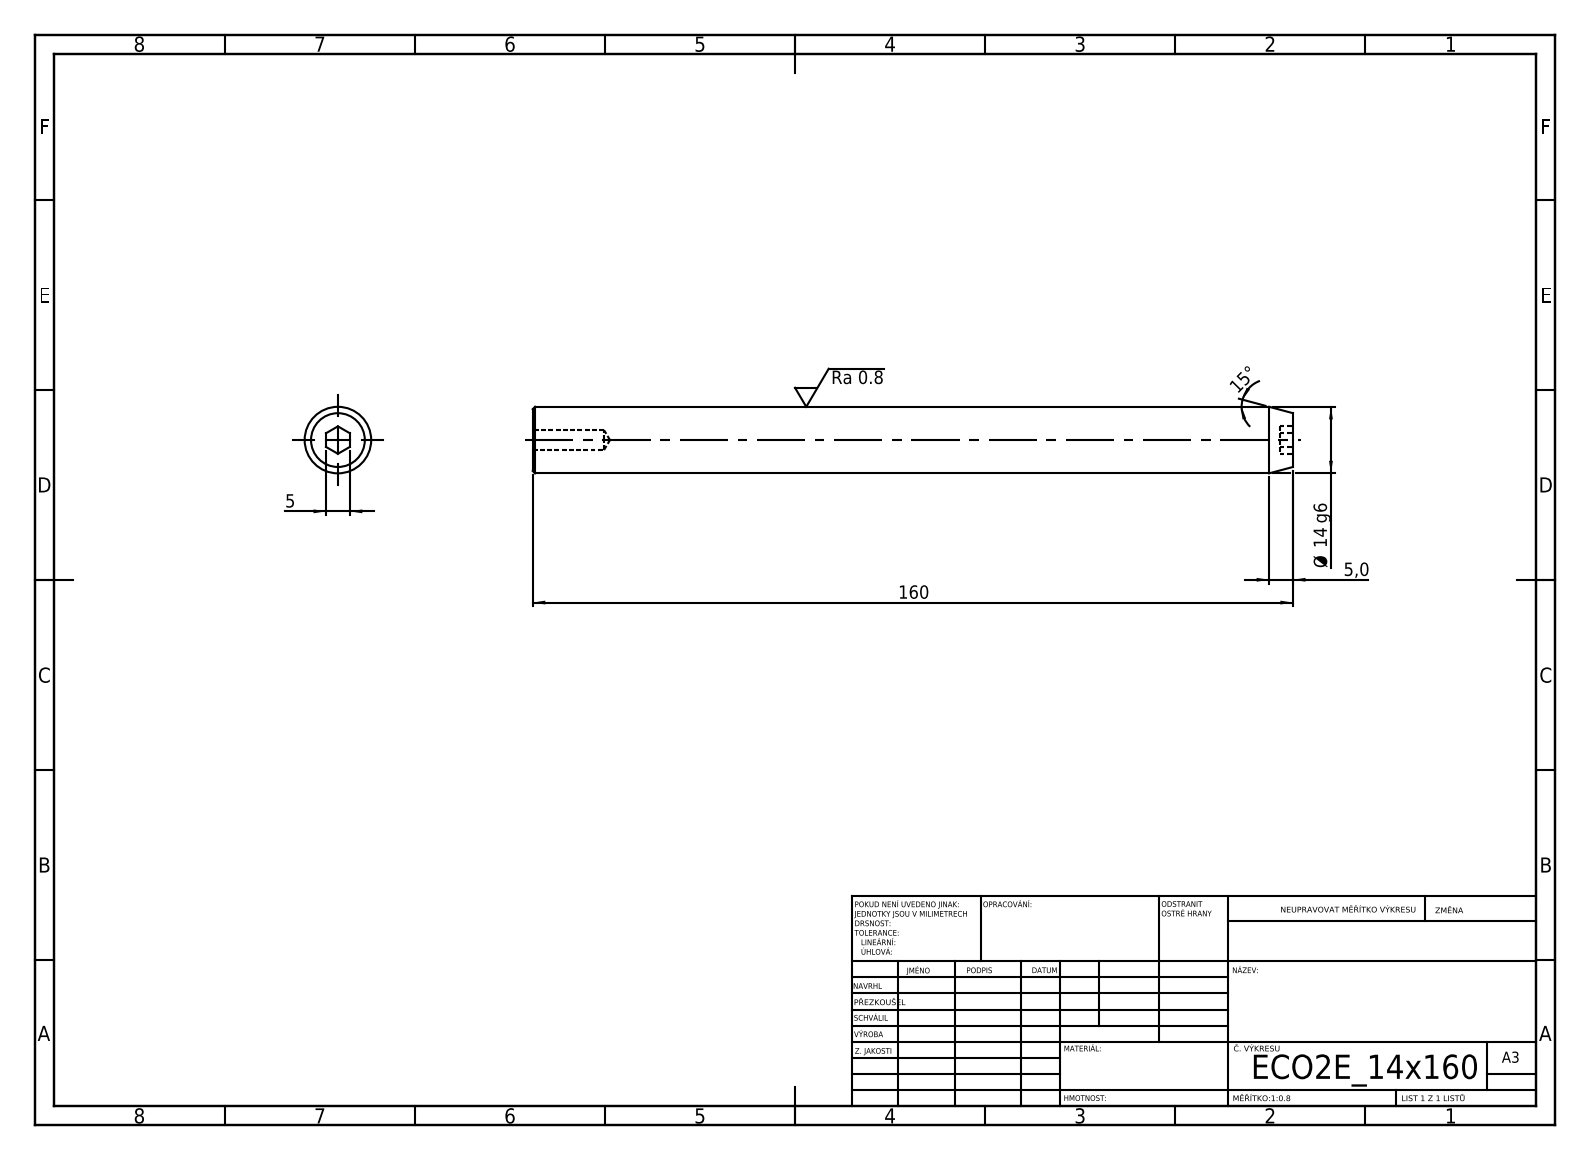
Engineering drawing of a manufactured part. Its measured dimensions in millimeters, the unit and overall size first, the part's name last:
Units: millimetres
Overall size (bounding box): 160 × 14 × 14
Round holes (diameter × count): ⌀4.2 ×1
Round bosses / shafts (diameter × count): ⌀14 ×1
Main face-to-face distances: 160, 5, 2.8, 157.2
Volume: 24 213 mm³ · Surface area: 7 513 mm²
Bodies: 1 solid, 19 faces (9 planar, 4 cylindrical, 6 other)
STEP written by: SolidWorks 2019 (CONFIG_CONTROL_DESIGN)
